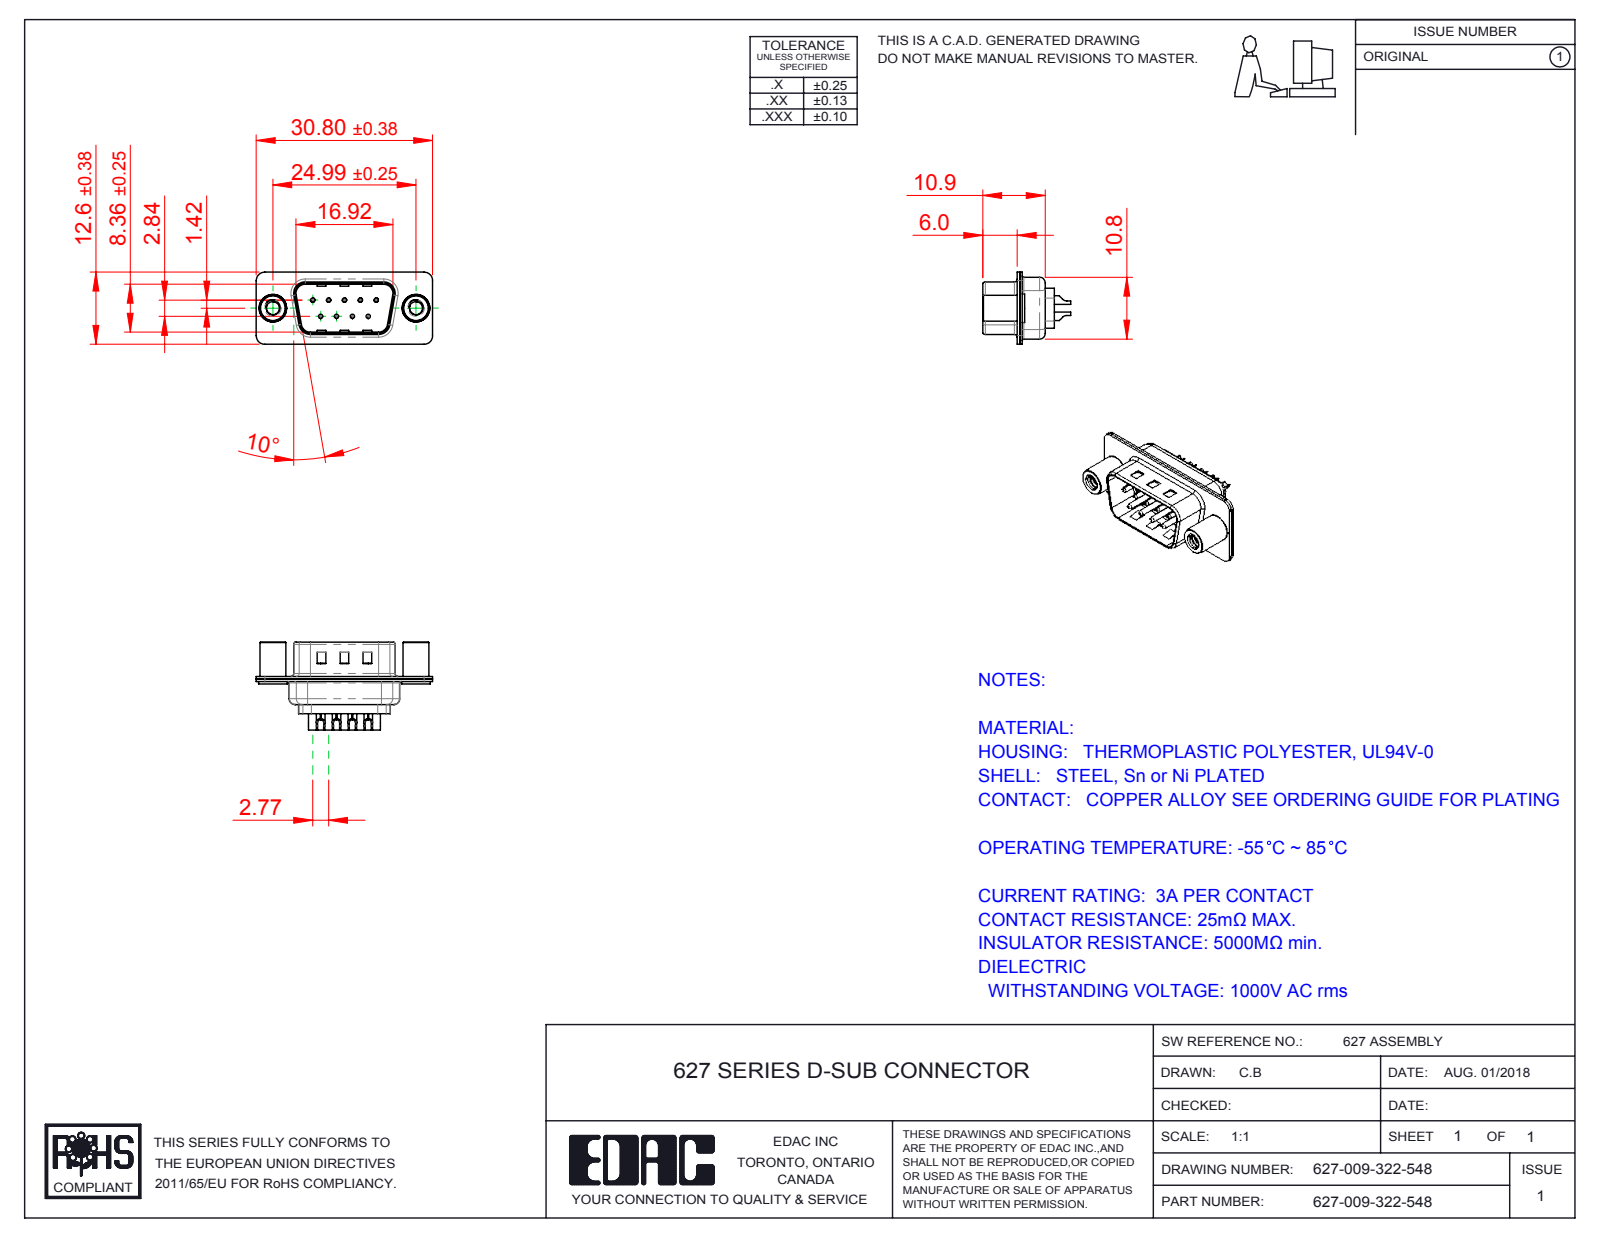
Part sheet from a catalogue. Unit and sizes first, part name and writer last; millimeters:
Units: millimetres
Overall size (bounding box): 30.8 × 15.35 × 12.6
Round holes (diameter × count): ⌀0.35 ×9, ⌀1.1 ×9, ⌀1.6 ×9, ⌀2.26 ×2, ⌀4 ×2, ⌀4.8 ×2
Round bosses / shafts (diameter × count): ⌀2 ×9, ⌀1.5 ×9, ⌀0.75 ×9, ⌀5 ×2, ⌀4.9 ×2, ⌀4.5 ×2
Partial cylindrical surfaces — rounded edges, fillets, slot ends (radius × count): R1.5 ×18, R2 ×12, R0.5 ×8, R1.6 ×8, R1 ×6, R0.25 ×4, R0.6 ×4, R0.65 ×4
Main face-to-face distances: 0.4, 0.45, 0.9, 0.82, 9.58, 1.4, 8.76, 0.5, 1.5, 6.5
Hole centre spacings: 3.16, 2.77, 5.54, 5.03, 5.04, 8.31, 7.48, 7.49
Volume: 1 379 mm³ · Surface area: 4 152 mm²
Bodies: 14 solids, 914 faces (235 planar, 418 cylindrical, 261 other)
Part name (STEP PRODUCT): 627 Shell Rear_09 Contacts; 627 Contact Row 1_22L; 627 Contact Row 2_22L; 627-009-322-548 (+3 more)
STEP written by: SolidWorks 2016 (CONFIG_CONTROL_DESIGN)
